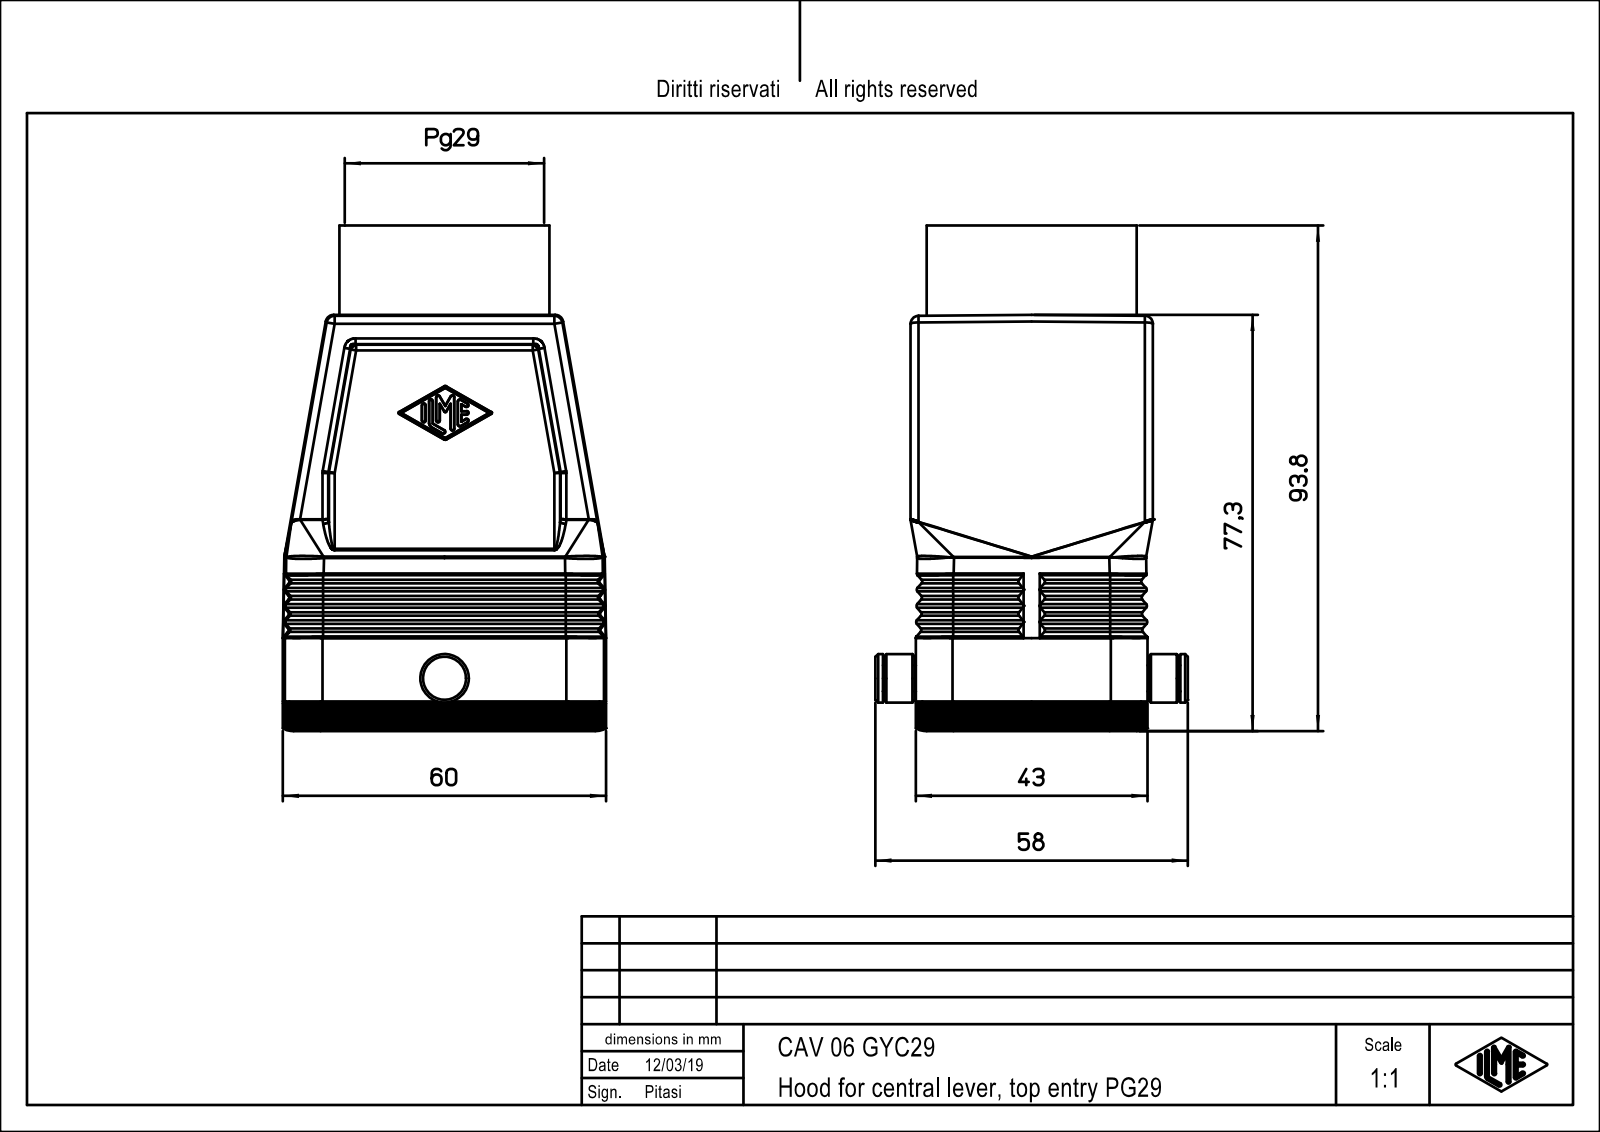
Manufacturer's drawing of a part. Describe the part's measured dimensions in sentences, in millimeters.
The part is named "CAV_06_GYC29". Its 3-D file was written by "PTC Creo Elements/Direct Modeling 19.0E 27-Jun-2016 (C) Parametric Technology GmbH (AUTOMOTIVE_DESIGN)". It is 1 solid with 533 faces: 175 planar, 178 cylindrical and 180 other. Overall it measures 93.75 by 60 by 58 millimeters. Its volume is 66 994 cubic millimeters and its surface area 36 098 square millimeters. Round holes: 4 of diameter 3, 1 of diameter 32, 1 of diameter 36.24. Round bosses or shafts: 1 of diameter 39, 1 of diameter 37, 1 of diameter 9, 1 of diameter 4.8. Partial cylindrical surfaces (rounded edges, fillets, slot ends): 54 of radius 0.5, 44 of radius 1.5, 12 of radius 3, 12 of radius 7, 4 of radius 4, 4 of radius 4.2, 4 of radius 5.8. The main face-to-face distances are 43, 7, 4, 2, 7.55, 1, 44, 60, 39, 5. The hole center spacings are 25.81, 27, 44, 51.62.
